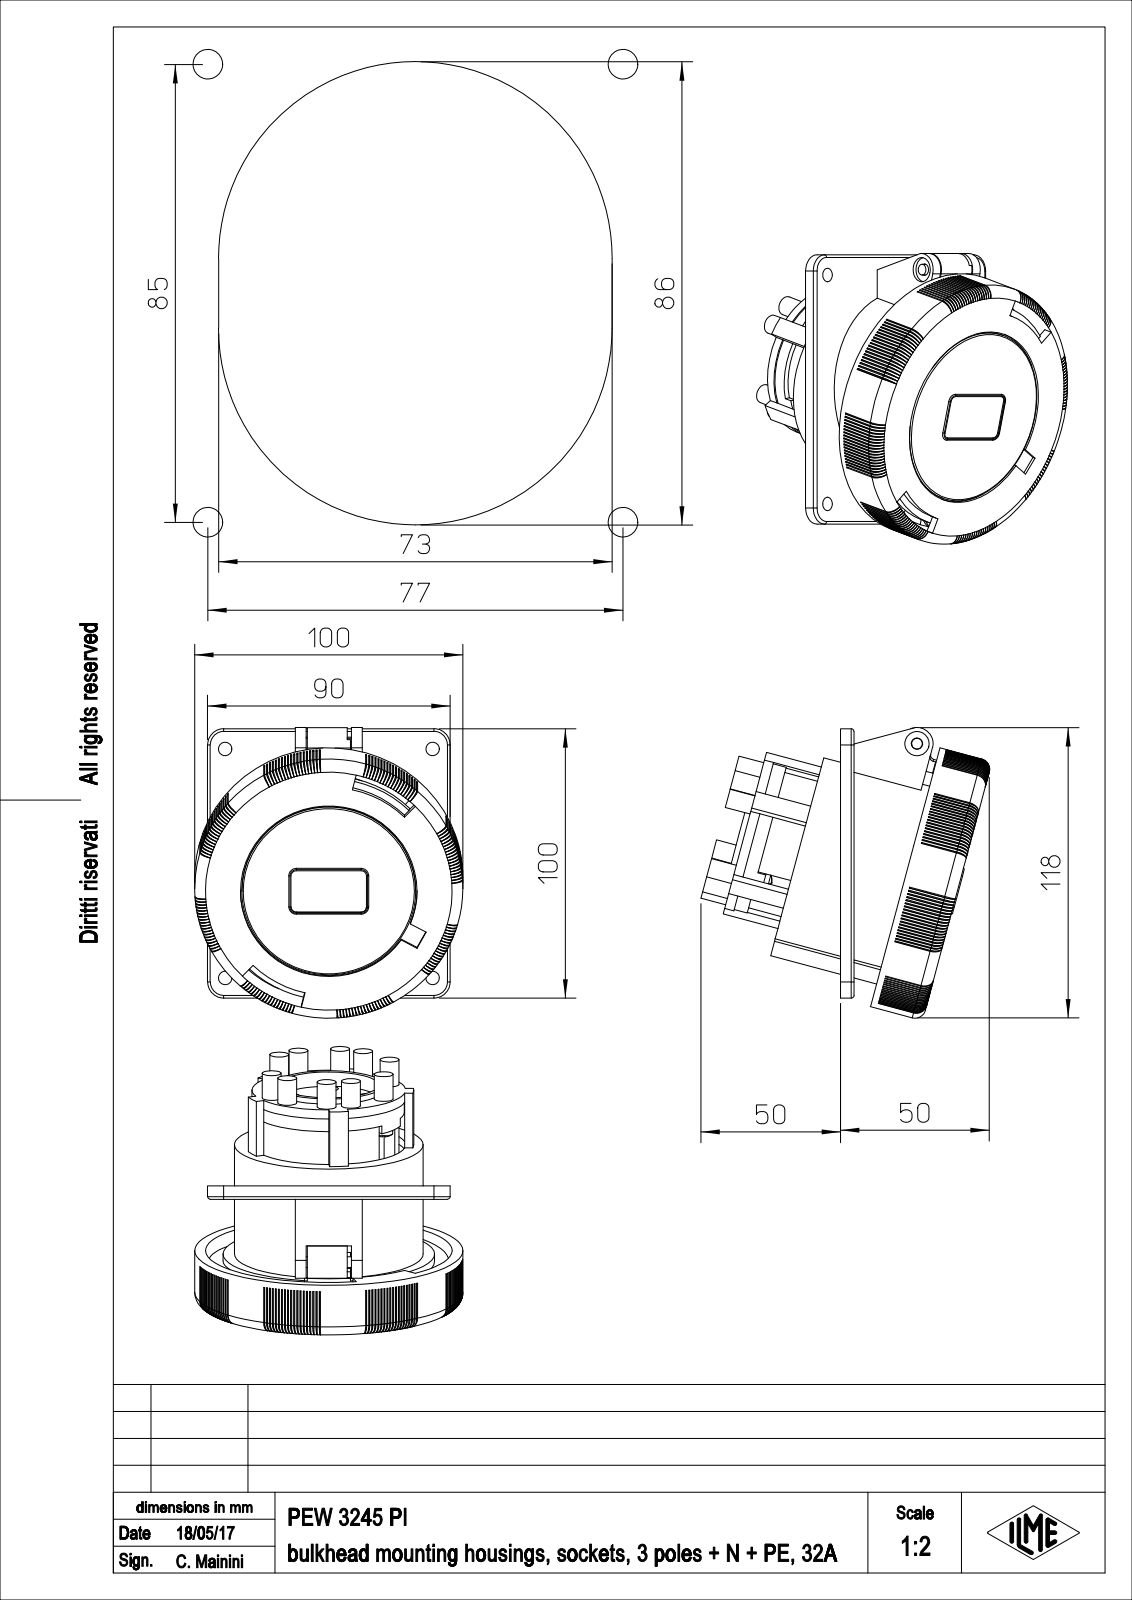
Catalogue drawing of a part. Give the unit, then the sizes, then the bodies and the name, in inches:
Units: inches
Overall size (bounding box): 4.248 × 4.216 × 3.917
Round holes (diameter × count): ⌀0.276 ×5, ⌀0.197 ×4, ⌀0.295 ×4, ⌀0.551 ×4, ⌀0.165 ×1, ⌀0.354 ×1, ⌀0.374 ×1, ⌀1.457 ×1, ⌀2.244 ×1, ⌀2.303 ×1, ⌀2.429 ×1, ⌀2.571 ×1
Round bosses / shafts (diameter × count): ⌀0.276 ×11, ⌀0.264 ×2, ⌀3.917 ×1, ⌀3.346 ×1, ⌀3.091 ×1, ⌀2.972 ×1, ⌀2.756 ×1, ⌀2.539 ×1
Partial cylindrical surfaces — rounded edges, fillets, slot ends (radius × count): R0.142 ×152, R0.236 ×6, R0.016 ×4, R0.039 ×4, R0.079 ×4, R0.008 ×3, R0.157 ×2, R1.024 ×2
Main face-to-face distances: 0.197, 0.118, 2.272, 0.079, 0.787, 0.669, 2.39, 1.602, 0.264, 0.441
Hole centre spacings: 1.134, 0.701, 0.596, 0.596, 0.597, 1.135, 0.701, 0.595
Volume: 16.46 in³ · Surface area: 162.9 in²
Bodies: 1 solid, 1440 faces (642 planar, 307 cylindrical, 491 other)
Part name (STEP PRODUCT): PEW_3245_PI
STEP written by: PTC Creo Elements/Direct Modeling 19.0E 27-Jun-2016 (C) Parametric Technology GmbH (AUTOMOTIVE_DESIGN)
